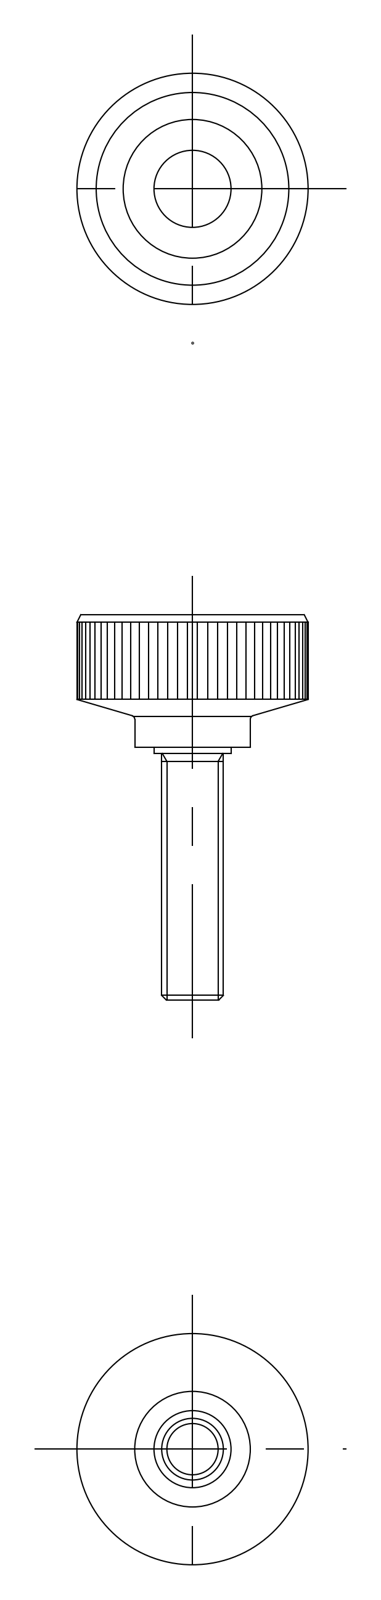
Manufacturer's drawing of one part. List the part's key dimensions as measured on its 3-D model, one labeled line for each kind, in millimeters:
Part name (STEP PRODUCT): screw; knob; KKM_30_M8_32_5573_36
STEP written by: CADfix (AUTOMOTIVE_DESIGN)
Units: millimetres
Bodies: 2 solids, 35 faces (0 planar, 0 cylindrical, 35 other)
Overall size (bounding box): 50 × 30 × 30
Volume: 8 347 mm³ · Surface area: 4 494 mm²
